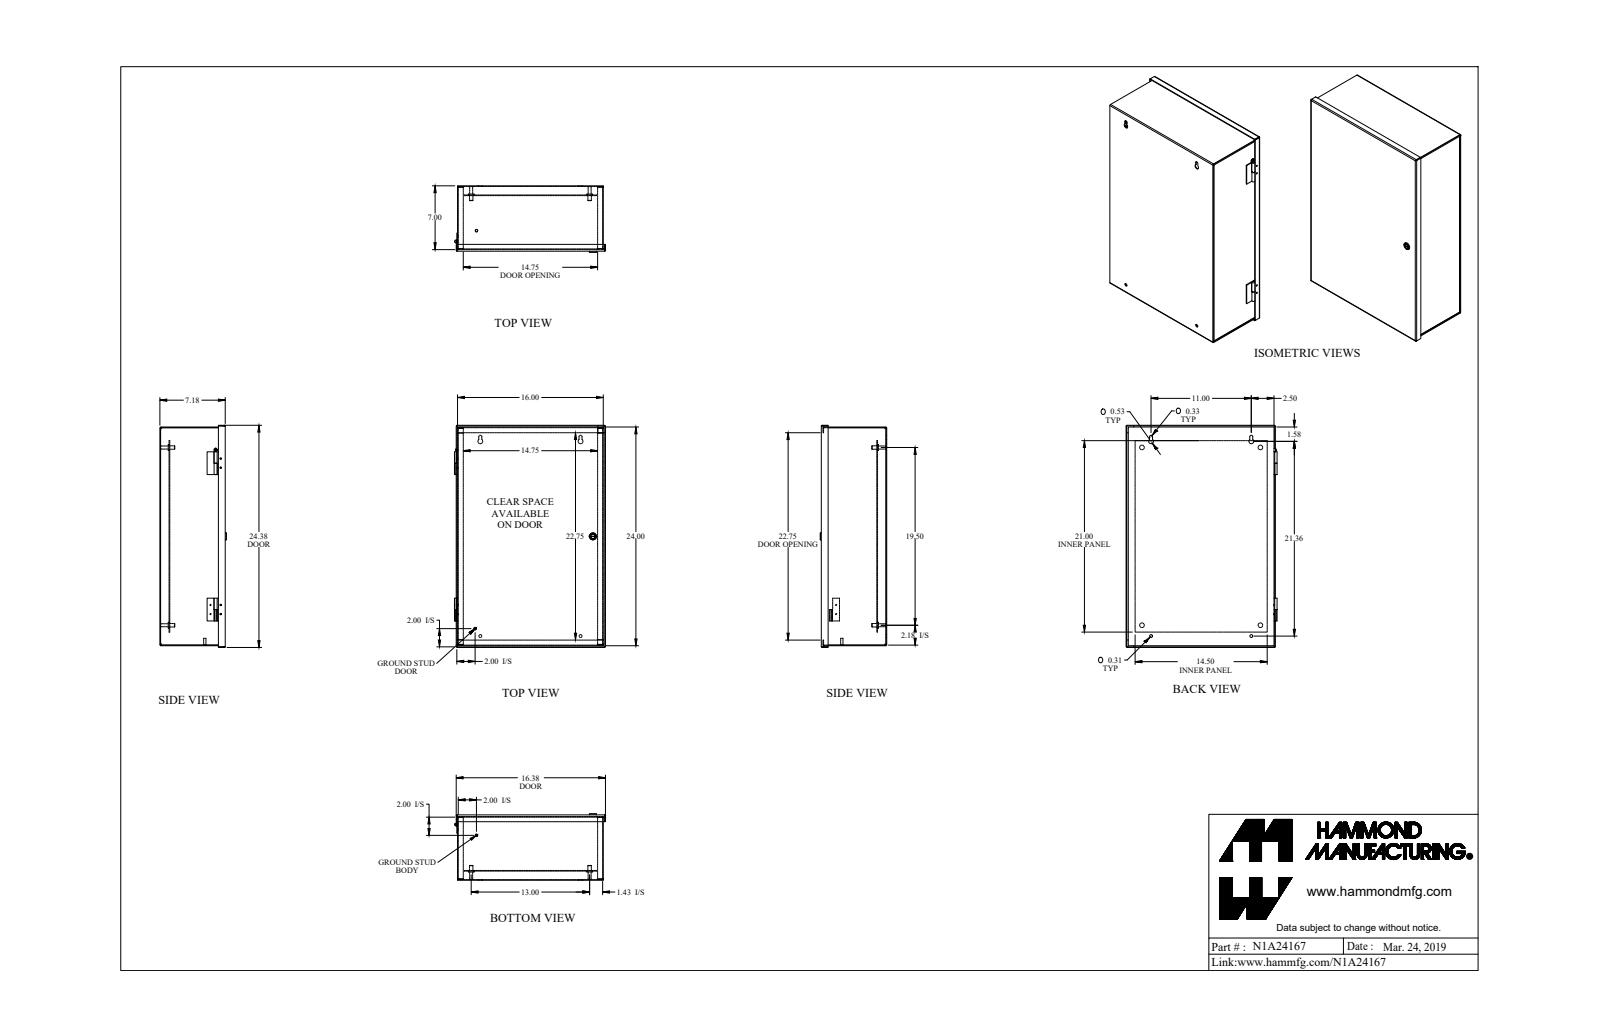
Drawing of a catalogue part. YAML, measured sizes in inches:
part_name: "N1A24167"
step_written_by: "SolidWorks 2018 (AUTOMOTIVE_DESIGN)"
units: inches
bodies: {solids: 23, faces: 520, planar: 294, cylindrical: 182, other: 44}
overall_size: [24.384, 16.574, 7.299]
volume: 129.8
surface_area: 3618
round_holes:
  - {diameter: 0.14, count: 8}
  - {diameter: 0.5, count: 4}
  - {diameter: 0.307, count: 2}
  - {diameter: 0.312, count: 2}
  - {diameter: 0.445, count: 2}
  - {diameter: 0.17, count: 1}
  - {diameter: 0.187, count: 1}
  - {diameter: 0.516, count: 1}
round_bosses_or_shafts:
  - {diameter: 0.128, count: 8}
  - {diameter: 0.375, count: 5}
  - {diameter: 0.65, count: 4}
  - {diameter: 0.33, count: 4}
  - {diameter: 1, count: 2}
  - {diameter: 0.281, count: 2}
  - {diameter: 0.25, count: 2}
  - {diameter: 0.788, count: 1}
partial_cylinders:
  - {radius: 0.036, count: 16}
  - {radius: 0.108, count: 16}
  - {radius: 0.06, count: 2}
  - {radius: 0.153, count: 2}
  - {radius: 0.164, count: 2}
  - {radius: 0.266, count: 2}
  - {radius: 0.03, count: 1}
  - {radius: 0.125, count: 1}
face_to_face_distances: [0.072, 7.105, 1.009, 6.096, 7.033, 7.177, 15.928, 1.081, 6.024, 0.937]
hole_center_spacings: [1, 1.119, 1.104, 1.553, 2.031, 9.757, 12.059, 13]
